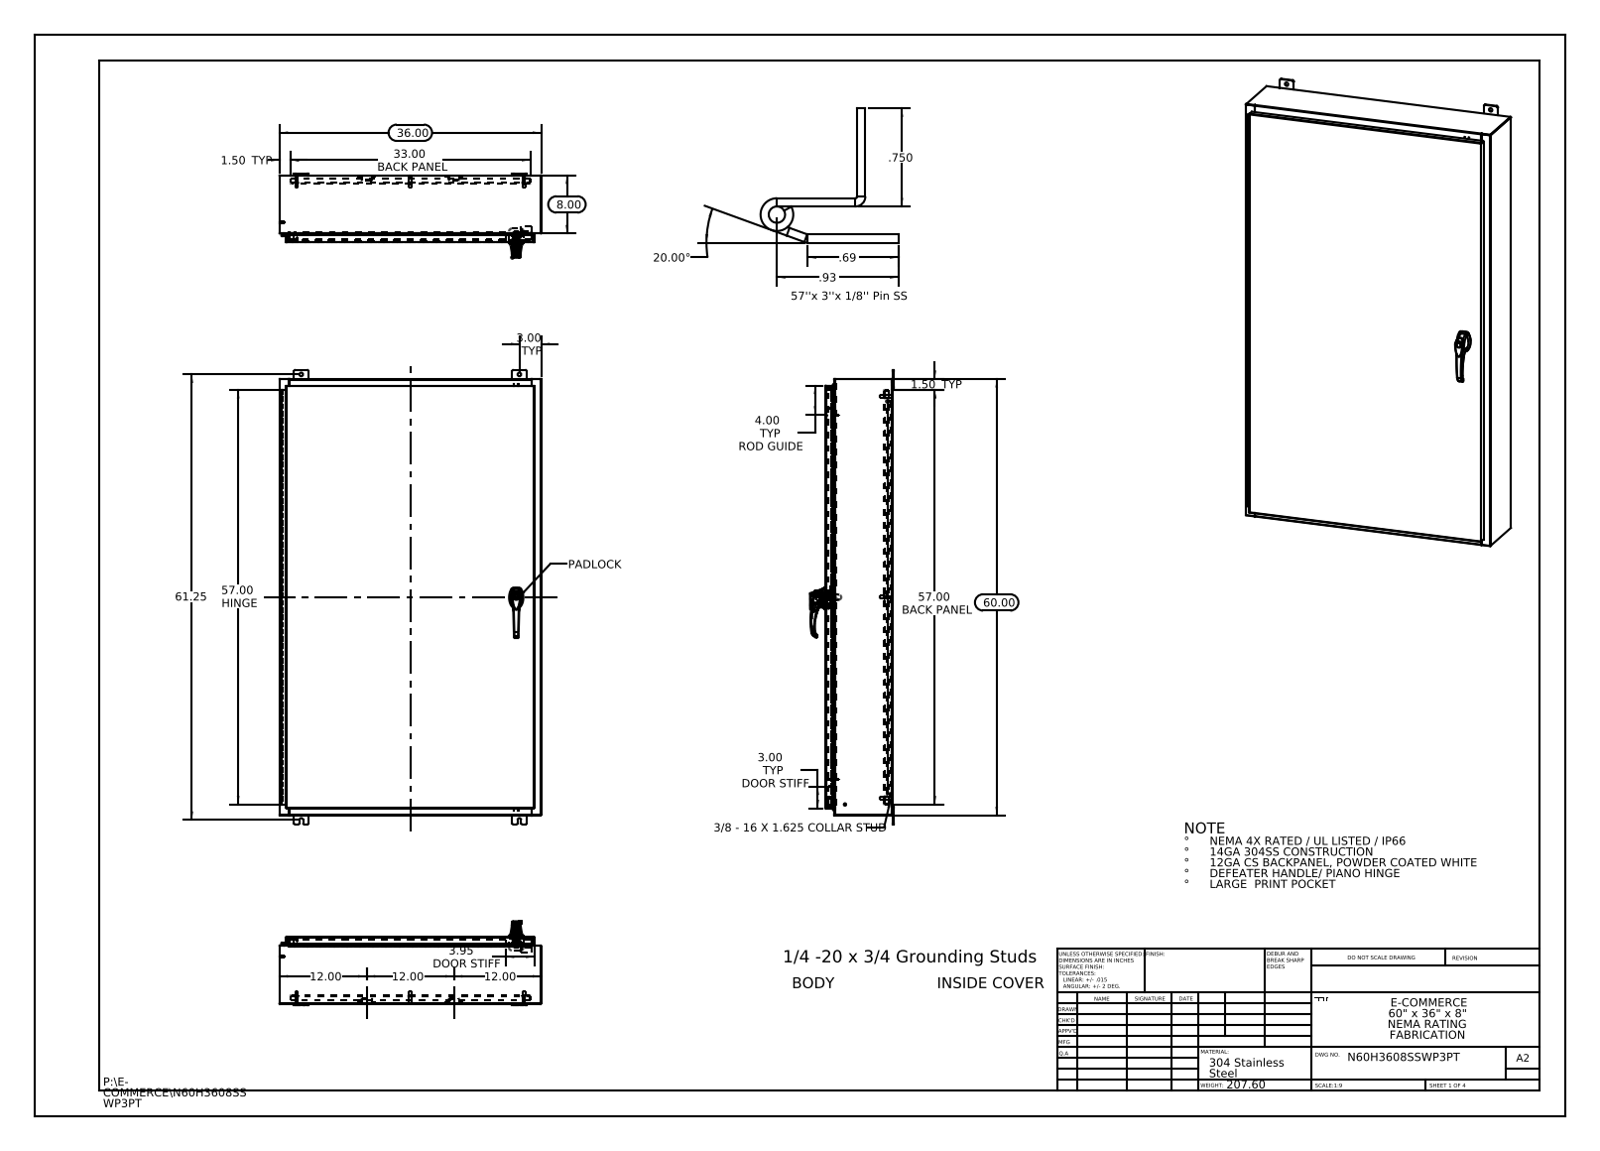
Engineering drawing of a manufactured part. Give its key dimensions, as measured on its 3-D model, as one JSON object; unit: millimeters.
{"part_name": "00005310_26163101; N60H3608SSWP3PT Enclosure Stiffener; 26161102; 2616310101 (+8 more)", "step_written_by": "SolidWorks 2013 (CONFIG_CONTROL_DESIGN)", "units": "millimeters", "bodies": {"solids": 51, "faces": 3688, "planar": 1453, "cylindrical": 1449, "other": 786}, "overall_size": [1587.5, 914.4, 292], "volume_mm3": 12150000, "surface_area_mm2": 11800000, "round_holes": [[12.7, 12], [6.4, 10], [3.5, 3], [4.1, 3], [2, 2], [5.2, 2], [8, 2], [11.1, 2], [3.2, 1], [3.2, 1], [5, 1], [7, 1]], "round_bosses_or_shafts": [[4, 10], [3.6, 10], [15.9, 8], [9.5, 8], [8.4, 8], [8, 3], [6, 3], [30, 1]], "partial_cylinders_radius": [[3, 37], [0.3, 34], [0.2, 33], [2.2, 28], [4.8, 24], [1, 15], [0.7, 12], [0.2, 6]], "face_to_face_distances": [1.9, 231.8, 229.9, 2.6, 233.7, 25.4, 206.4, 27.3, 204.5, 29.9], "hole_center_spacings": [593.2, 651.8, 701.7, 1059.4, 1458.4, 786.8, 793.8, 1403.4]}
